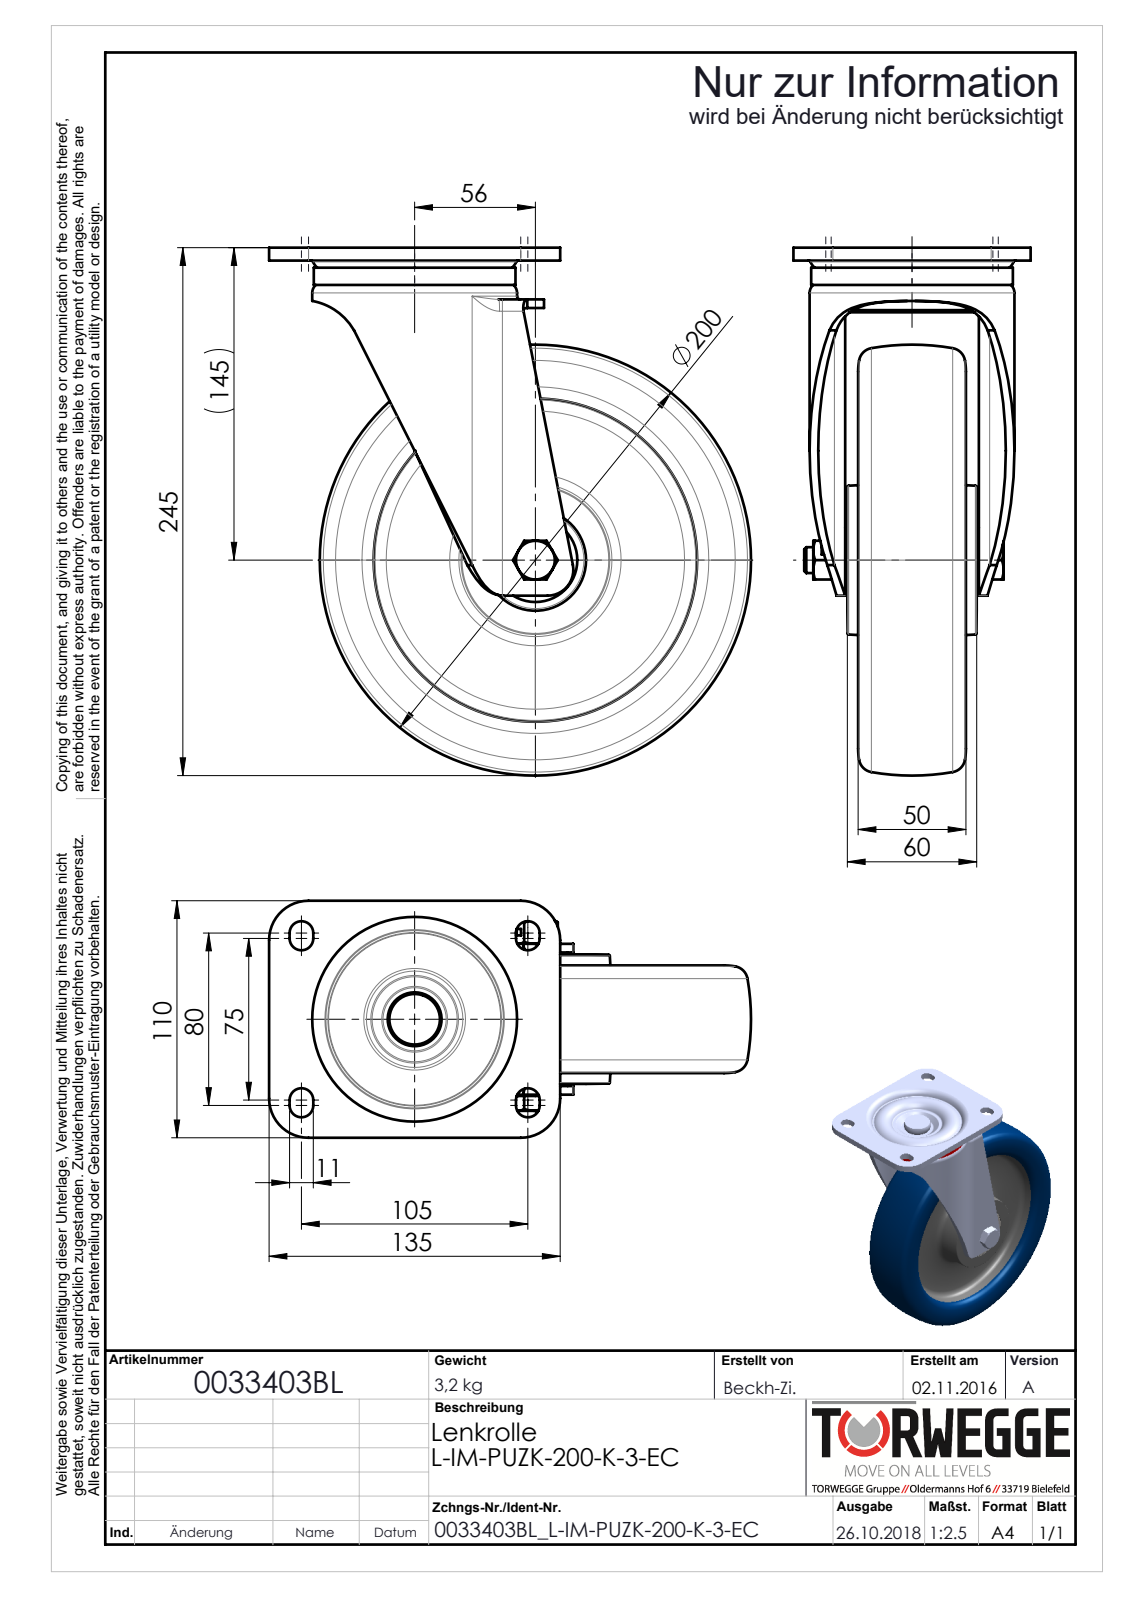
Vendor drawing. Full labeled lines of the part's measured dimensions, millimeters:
Part name (STEP PRODUCT): 0033403_L-IM-PUZK-200-K-3-EC
STEP written by: SolidWorks 2016 (AUTOMOTIVE_DESIGN)
Units: millimetres
Bodies: 0 solids, 329 faces (144 planar, 61 cylindrical, 124 other)
Overall size (bounding box): 243.37 × 223.5 × 110
Round holes (diameter × count): ⌀12 ×1, ⌀87 ×1
Round bosses / shafts (diameter × count): ⌀95 ×1, ⌀93.54 ×1, ⌀61.97 ×1, ⌀18 ×1
Partial cylindrical surfaces — rounded edges, fillets, slot ends (radius × count): R5.5 ×10, R0.86 ×4, R18.29 ×4, R0.62 ×3, R1.5 ×2, R12 ×2, R25 ×2, R29 ×2
Main face-to-face distances: 6, 4, 66, 24, 62, 70, 20, 1.5, 5.5, 5
